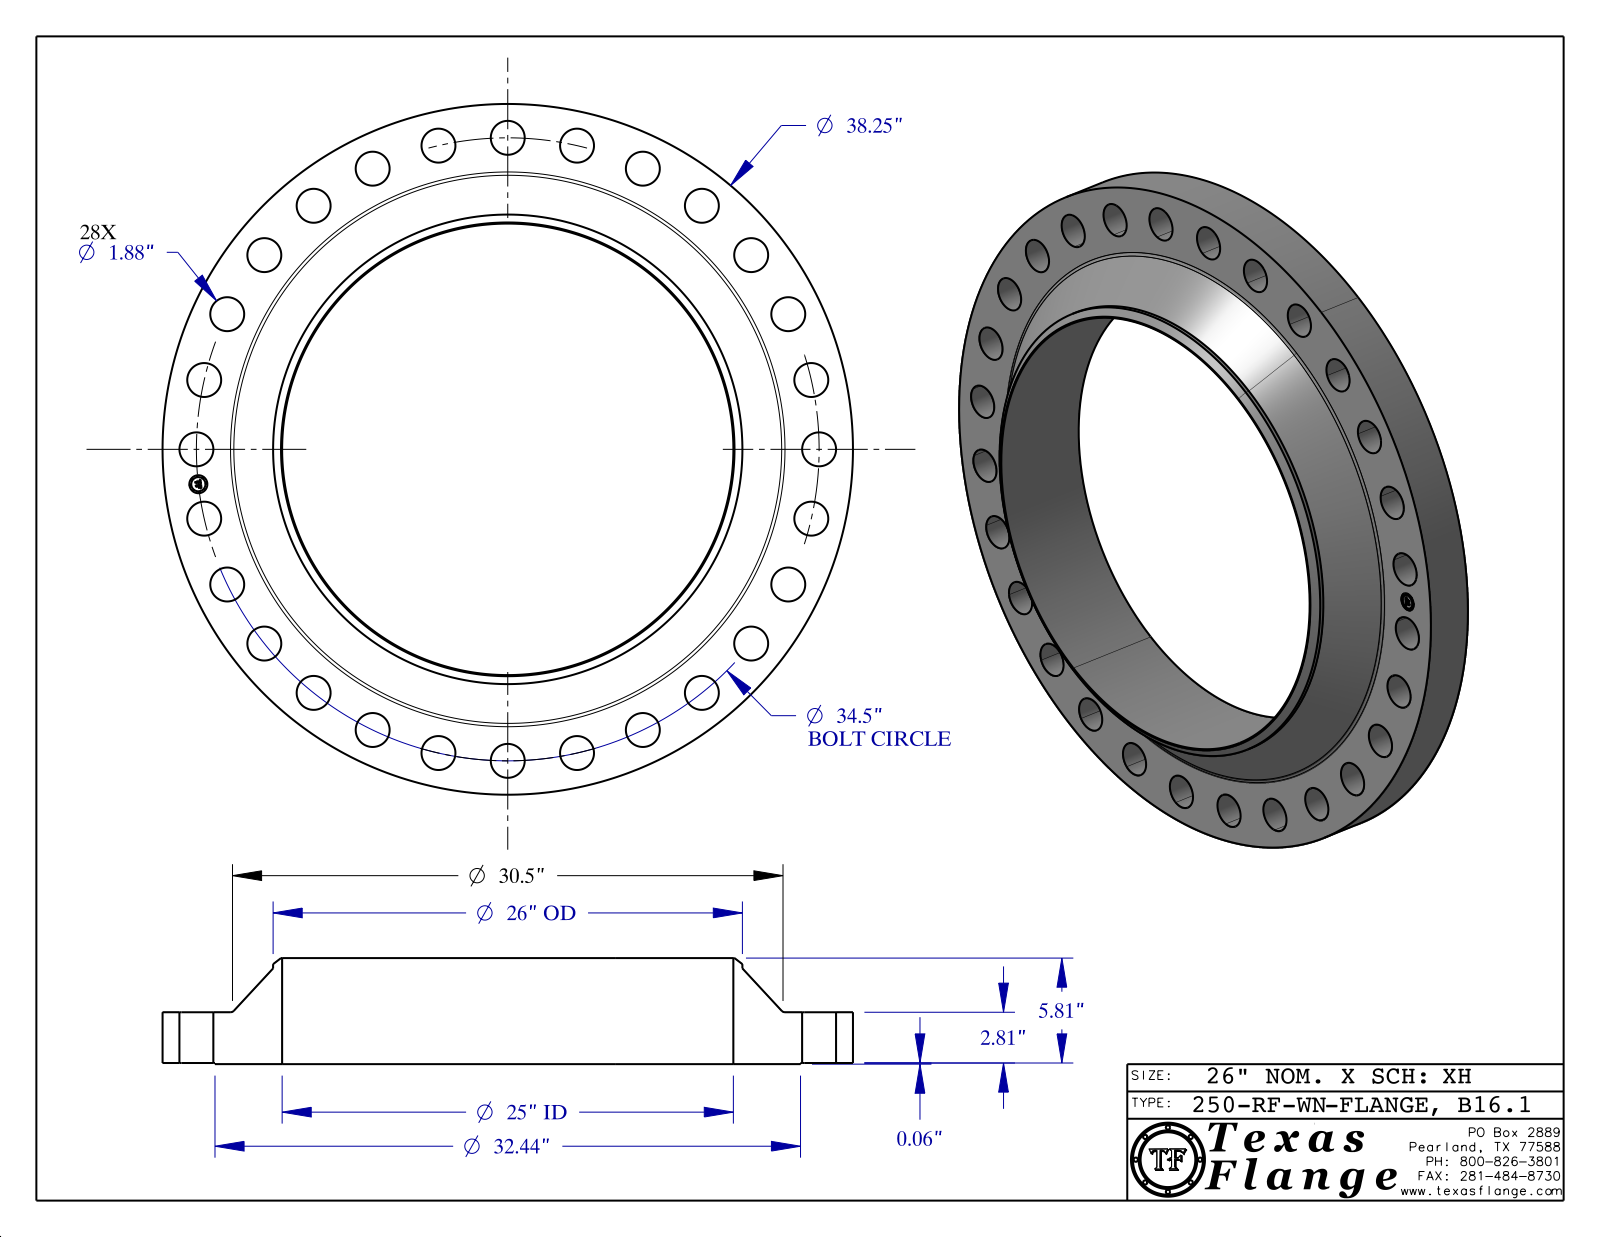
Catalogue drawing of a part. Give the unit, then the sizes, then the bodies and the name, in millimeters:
Units: millimetres
Overall size (bounding box): 971.55 × 971.55 × 149.16
Round holes (diameter × count): ⌀47.75 ×28, ⌀25.4 ×1, ⌀635 ×1
Round bosses / shafts (diameter × count): ⌀1.54 ×8, ⌀971.55 ×1, ⌀823.98 ×1, ⌀660.4 ×1, ⌀20.01 ×1
Main face-to-face distances: 72.96, 1.59, 71.37, 149.16, 147.57, 76.2, 0.38, 72.58, 70.99, 76.58
Hole centre spacings: 438.15, 685.12, 870.79, 380.21, 466.22, 827.12, 854.33, 289.42
Volume: 32 820 000 mm³ · Surface area: 1 647 000 mm²
Bodies: 1 solid, 459 faces (369 planar, 84 cylindrical, 6 other)
Part name (STEP PRODUCT): 250-RF-WN, B16.1
STEP written by: CATIA V5 STEP AP203 (CONFIG_CONTROL_DESIGN)
